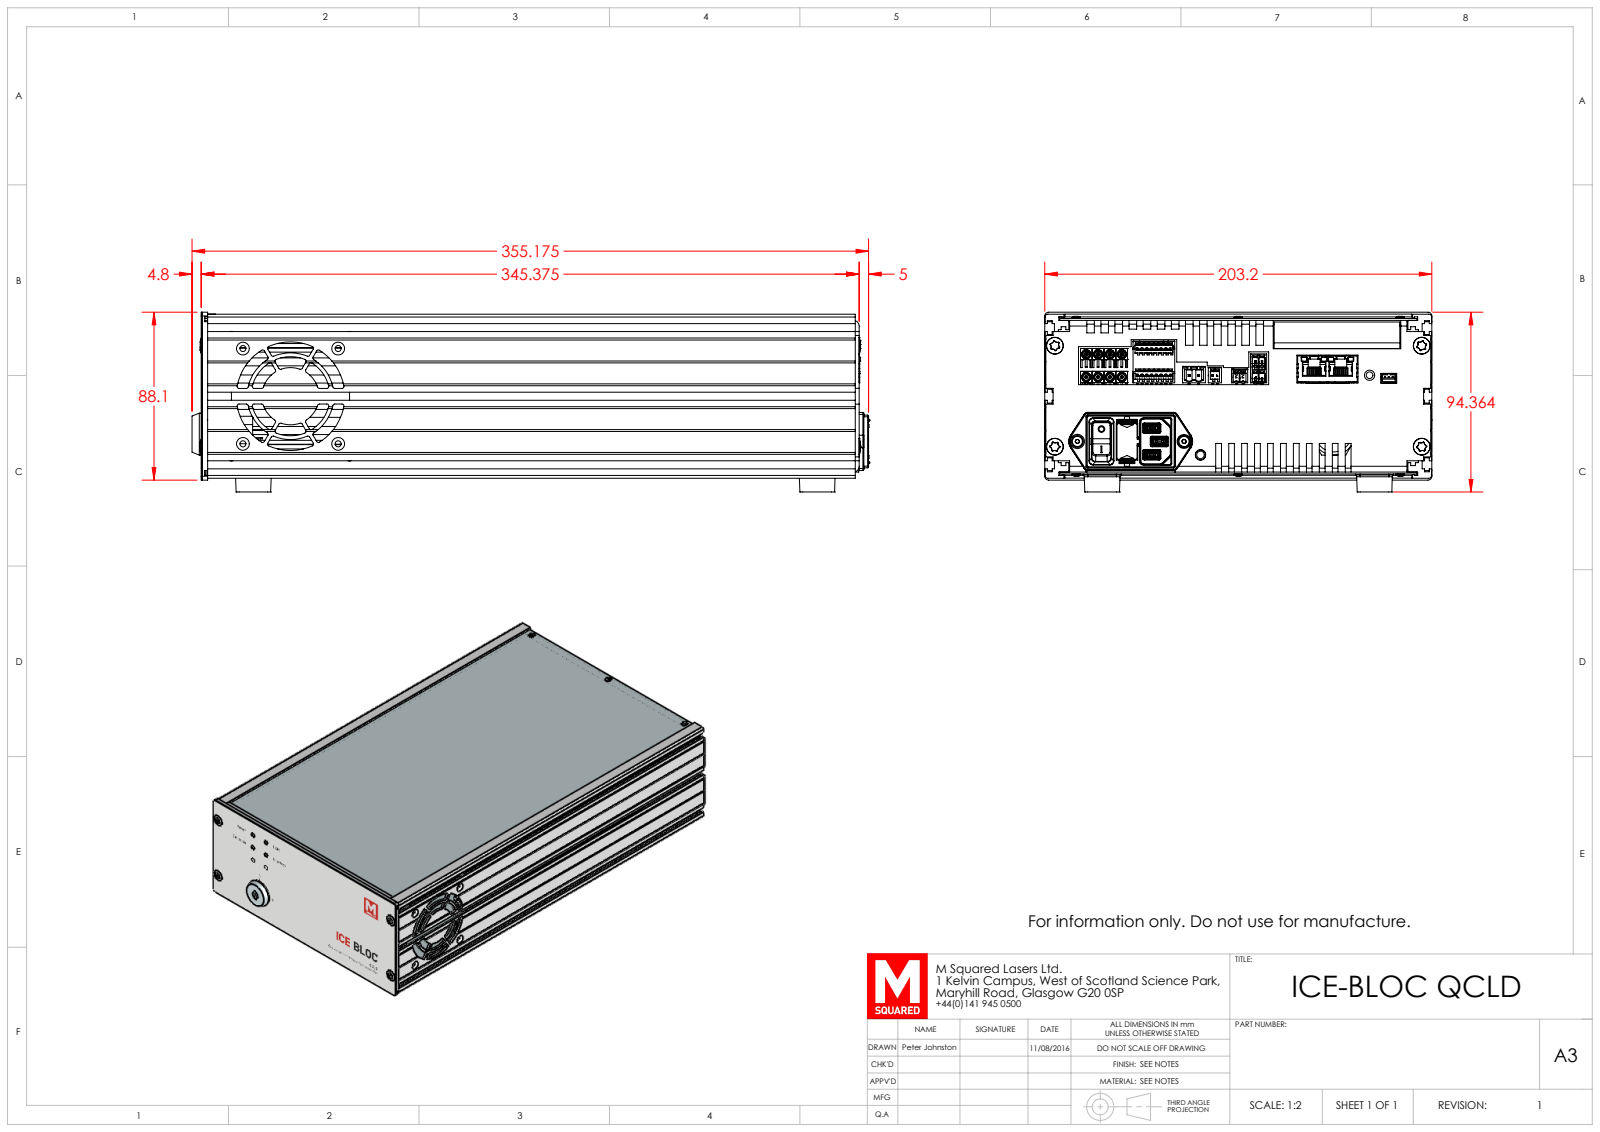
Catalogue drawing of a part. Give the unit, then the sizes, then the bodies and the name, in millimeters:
Units: millimetres
Overall size (bounding box): 355.77 × 203.2 × 94.36
Round holes (diameter × count): ⌀3.42 ×8, ⌀3.2 ×4, ⌀3.5 ×4, ⌀9 ×4, ⌀2 ×3, ⌀6.3 ×2, ⌀2.5 ×1, ⌀5.4 ×1, ⌀7.3 ×1, ⌀7.5 ×1
Round bosses / shafts (diameter × count): ⌀4.9 ×8, ⌀4.4 ×3, ⌀2.4 ×3, ⌀5.35 ×2, ⌀22 ×1, ⌀4 ×1, ⌀3.5 ×1
Partial cylindrical surfaces — rounded edges, fillets, slot ends (radius × count): R0.2 ×68, R1 ×50, R2 ×48, R0.5 ×30, R1.16 ×20, R2.5 ×16, R1.5 ×13, R2 ×11
Main face-to-face distances: 1, 80.56, 81.56, 79.56, 203, 12.5, 3, 190.5, 0.38, 3.38
Hole centre spacings: 6.25, 11.99, 13.52, 50, 6.26, 12, 12.5, 12.51
Bodies: 0 solids, 2067 faces (1246 planar, 562 cylindrical, 259 other)
Part name (STEP PRODUCT): ICE-BLOC QCL
STEP written by: SolidWorks 2015 (AUTOMOTIVE_DESIGN)
